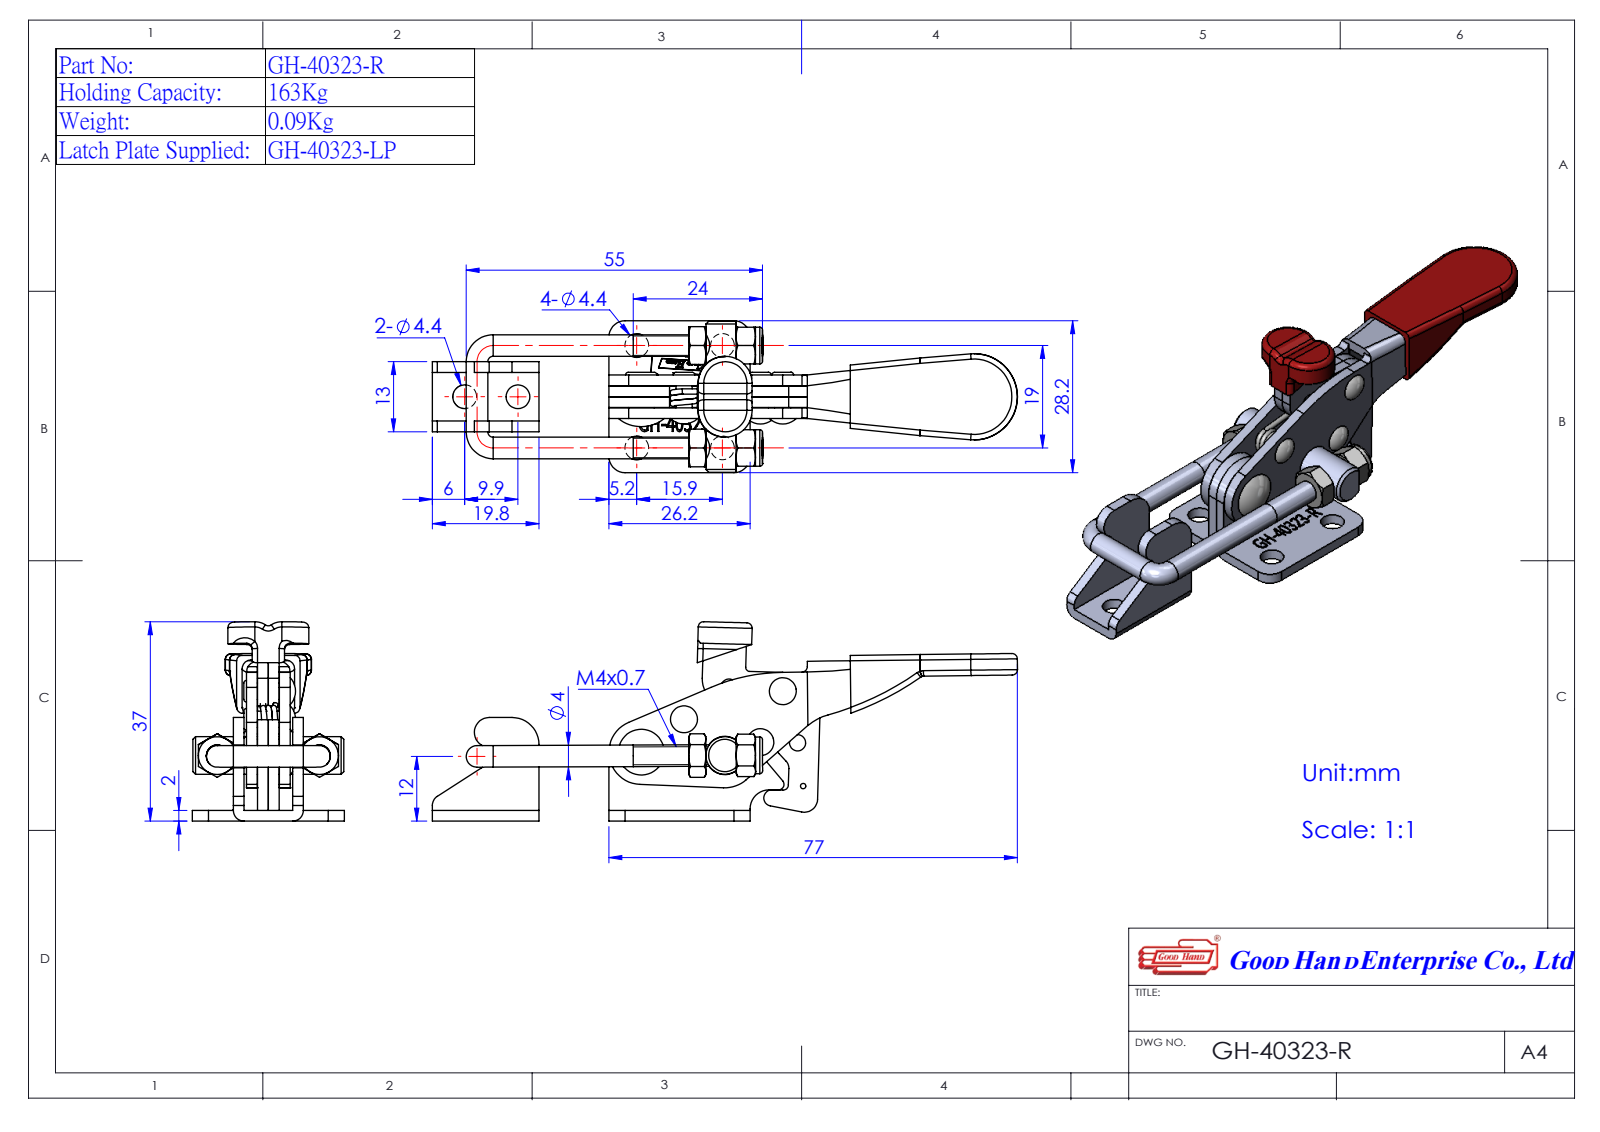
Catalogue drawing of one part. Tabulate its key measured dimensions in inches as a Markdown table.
| quantity | value |
| --- | --- |
| part name | Group4^GH-40323-R(簡化); Group3^GH-40323-R(簡化); Group2^GH-40323-R(簡化); 140323LP-1^GH-40323-R(簡化) (+2 more) |
| STEP written by | SolidWorks 2016 (AUTOMOTIVE_DESIGN) |
| units | inches |
| bodies | 7 solids, 799 faces (377 planar, 151 cylindrical, 271 other) |
| overall size | 4.277 × 1.457 × 1.11 |
| volume | 0.827 in³ |
| surface area | 20.3 in² |
| round holes (diameter × count) | 0.173 × 6, 0.13 × 2, 0.157 × 2, 0.165 × 2, 0.053 × 1, 0.15 × 1 |
| round bosses / shafts (diameter × count) | 0.157 × 3, 0.268 × 2, 0.118 × 2, 0.276 × 1, 0.05 × 1 |
| partial cylindrical surfaces (radius × count) | 0.039 × 8, 0.079 × 6, 0.118 × 4, 0.138 × 4, 0.197 × 4, 0.02 × 3, 0.021 × 3, 0.236 × 3 |
| main face-to-face distances | 0.079, 0.159, 0.081, 0.096, 0.337, 0.238, 0.24, 0.157, 0.335, 0.161 |
| hole center spacings | 0.748, 0.626, 0.945, 0.976, 1.312, 1.54, 1.92, 0.281 |
